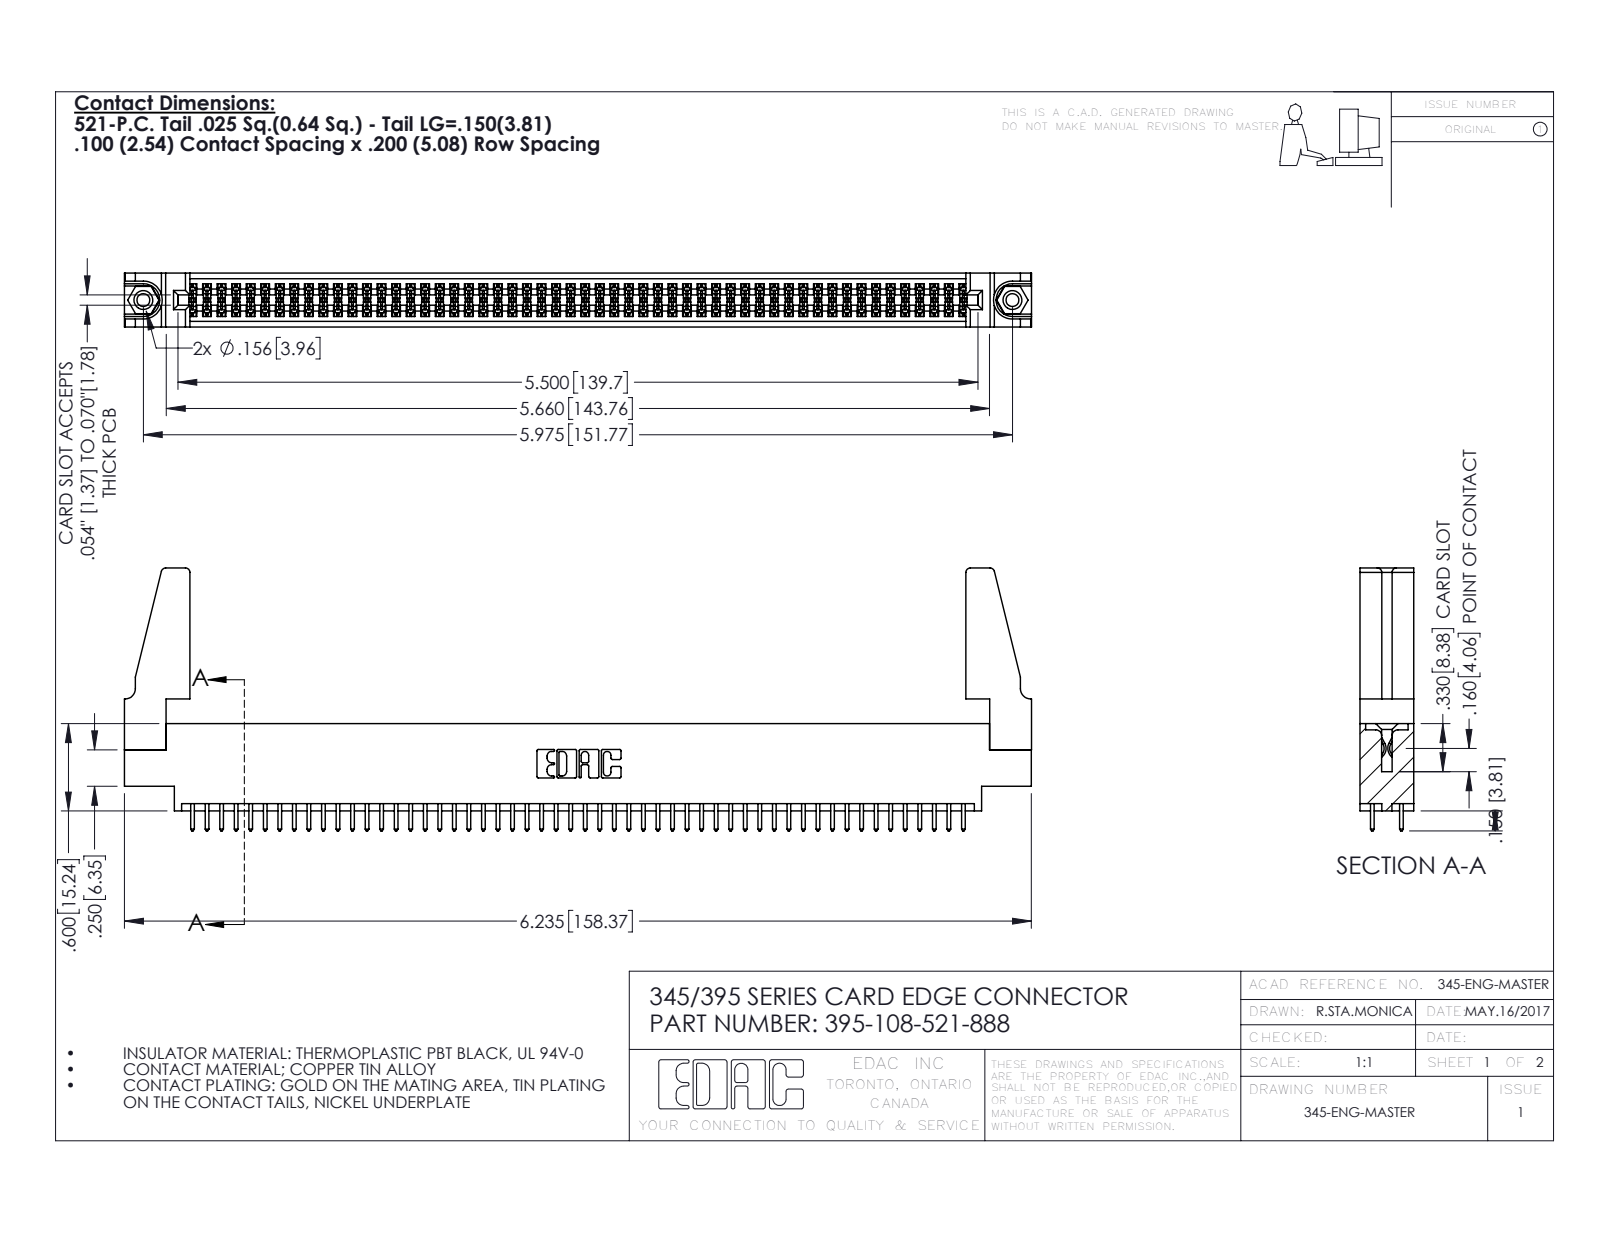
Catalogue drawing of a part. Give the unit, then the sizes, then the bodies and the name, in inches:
Units: inches
Overall size (bounding box): 6.236 × 1.807 × 0.37
Round holes (diameter × count): ⌀0.089 ×2, ⌀0.125 ×2, ⌀0.156 ×2, ⌀0.064 ×1
Round bosses / shafts (diameter × count): ⌀0.155 ×2
Partial cylindrical surfaces — rounded edges, fillets, slot ends (radius × count): R0.006 ×162, R0.01 ×108, R0.01 ×22, R0.03 ×8, R0.007 ×6, R0.031 ×6, R0.026 ×3, R0.014 ×2
Main face-to-face distances: 0.072, 0.298, 0.37, 0.2, 0.098, 0.272, 0.025, 0.225, 0.175, 0.149
Hole centre spacings: 0.27, 5.739, 5.975
Volume: 1.135 in³ · Surface area: 40.12 in²
Bodies: 113 solids, 5654 faces (3720 planar, 1918 cylindrical, 16 other)
Part name (STEP PRODUCT): 345-292-001_345-293-121; 395-108-521-888; 345-220-078_345-220-088; 345-250-001_345-250-001-102 (+1 more)
STEP written by: SolidWorks 2016 (CONFIG_CONTROL_DESIGN)
